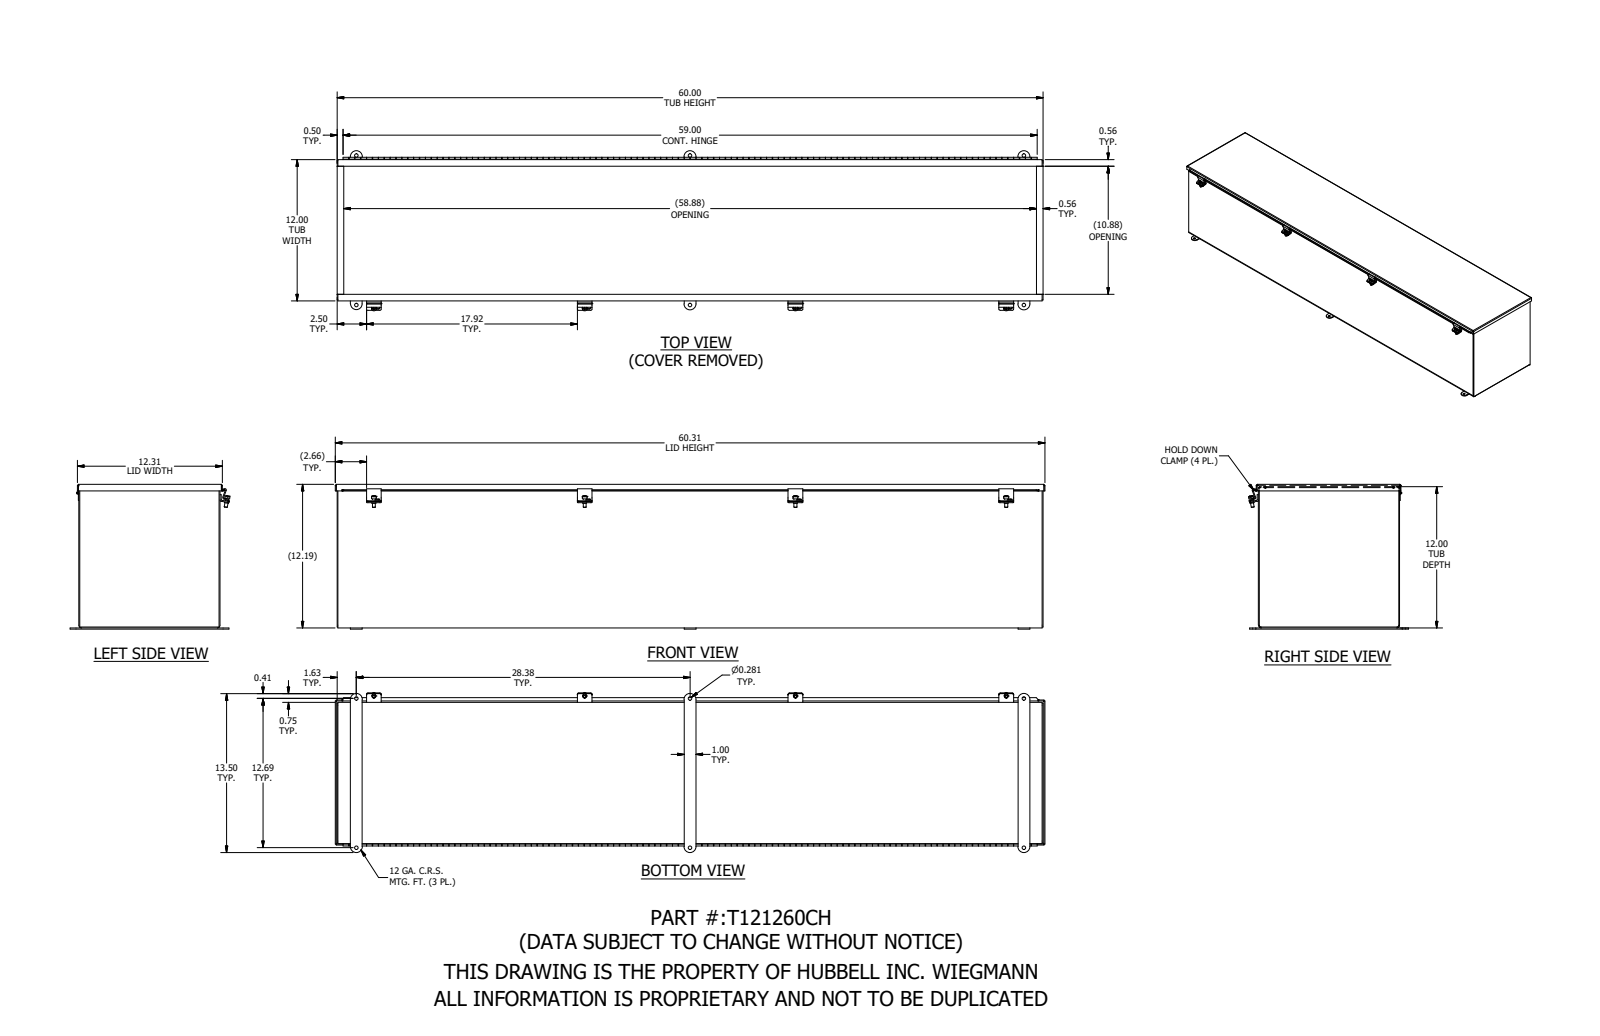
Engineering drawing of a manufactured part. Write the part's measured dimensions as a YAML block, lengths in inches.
part_name: "T121260CH"
step_written_by: "SolidWorks 2021 (AUTOMOTIVE_DESIGN)"
units: inches
bodies: {solids: 22, faces: 1221, planar: 592, cylindrical: 601, other: 28}
overall_size: [60.313, 13.595, 12.283]
volume: 253.7
surface_area: 6967
round_holes:
  - {diameter: 0.281, count: 6}
  - {diameter: 0.196, count: 4}
  - {diameter: 0.116, count: 1}
round_bosses_or_shafts:
  - {diameter: 0.41, count: 4}
  - {diameter: 0.344, count: 4}
  - {diameter: 0.25, count: 4}
  - {diameter: 0.2, count: 1}
  - {diameter: 0.1, count: 1}
partial_cylinders:
  - {radius: 0.125, count: 16}
  - {radius: 0.031, count: 9}
  - {radius: 0.105, count: 9}
  - {radius: 0.133, count: 8}
  - {radius: 0.5, count: 6}
  - {radius: 0.063, count: 3}
  - {radius: 0.126, count: 3}
  - {radius: 0.156, count: 2}
face_to_face_distances: [0.074, 11.926, 12.115, 12, 11.852, 12.189, 12.041, 59.926, 59.852, 60]
hole_center_spacings: [12.687, 17.917, 28.375, 28.375, 31.082, 31.083, 56.75, 58.151]
